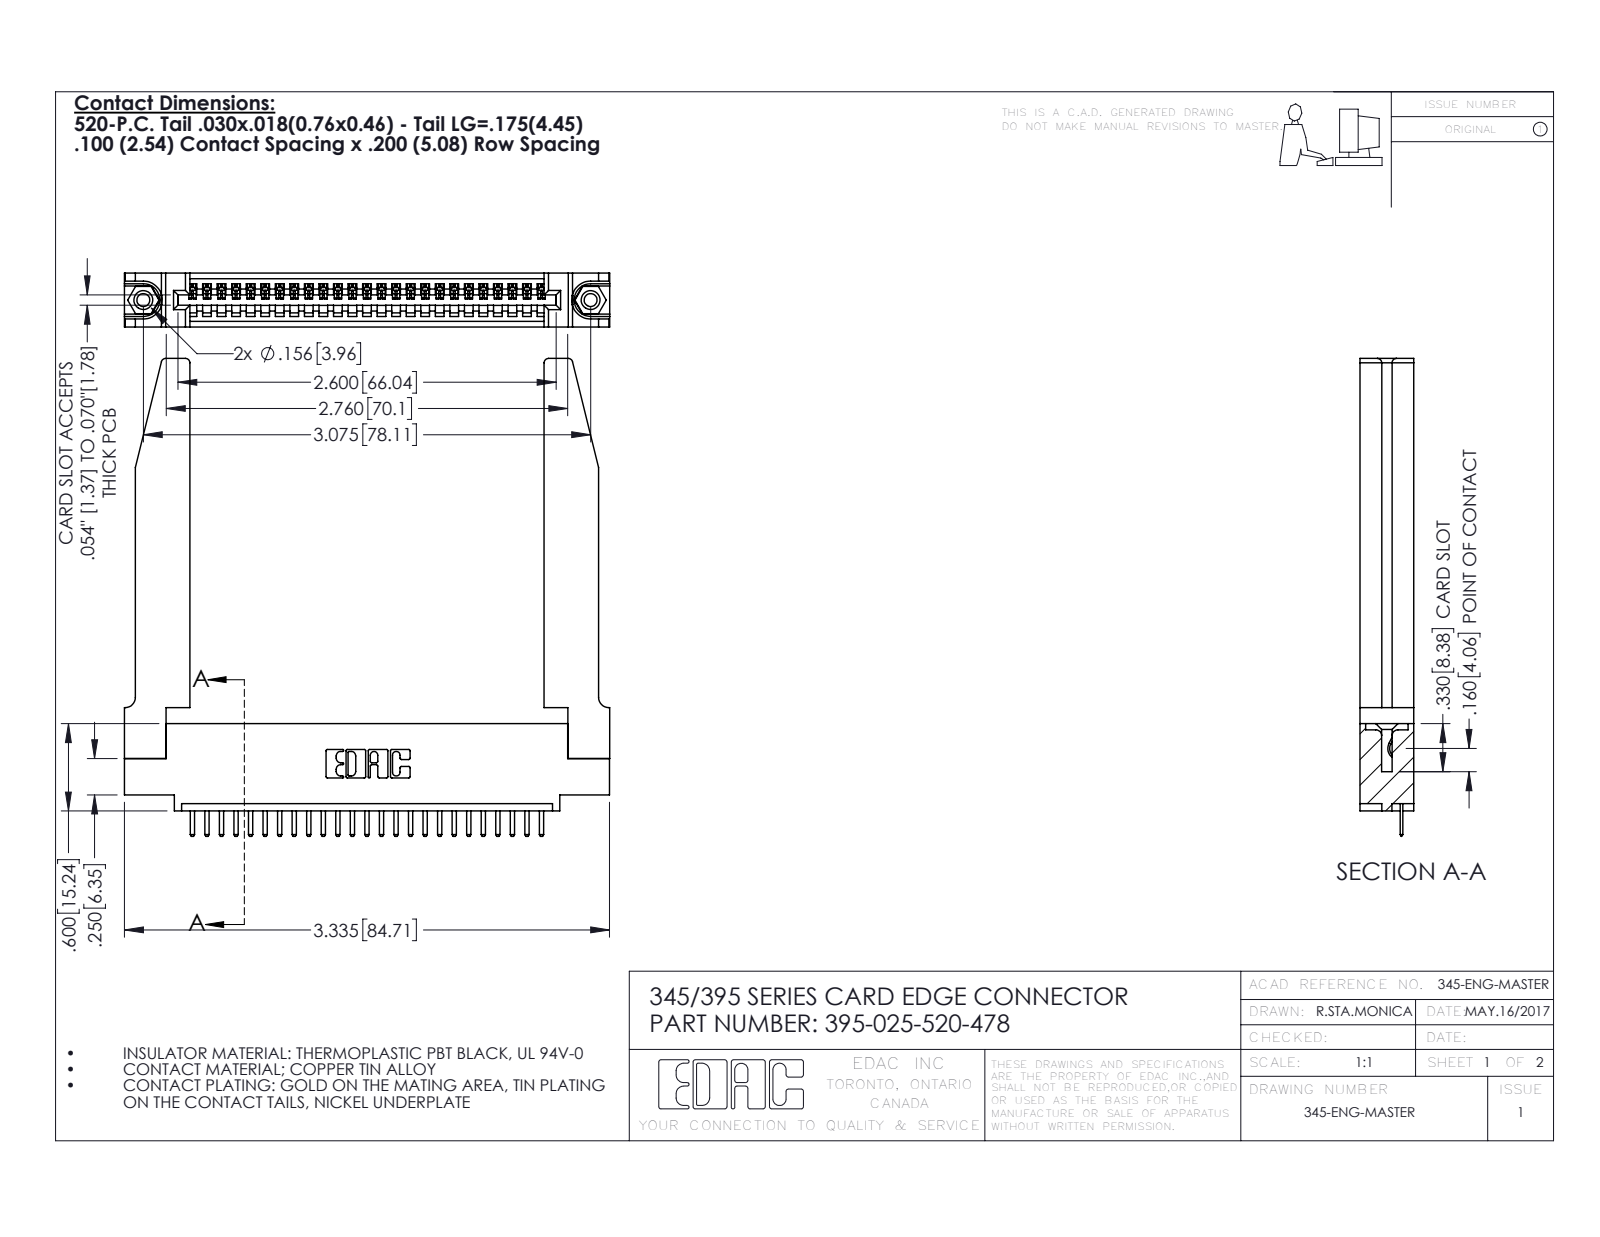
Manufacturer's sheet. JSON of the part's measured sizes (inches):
{"part_name": "395-025-520-478; 345-292-001_345-293-120; 345-250-001_345-250-001-102; 345-220-078_345-220-078 (+1 more)", "step_written_by": "SolidWorks 2016 (CONFIG_CONTROL_DESIGN)", "units": "inches", "bodies": {"solids": 30, "faces": 1914, "planar": 1276, "cylindrical": 586, "other": 52}, "overall_size": [3.336, 3.285, 0.37], "volume_in3": 0.948, "surface_area_in2": 26.01, "round_holes": [[0.089, 2], [0.125, 2], [0.156, 2], [0.064, 1]], "round_bosses_or_shafts": [[0.155, 2]], "partial_cylinders_radius": [[0.01, 52], [0.006, 50], [0.01, 22], [0.03, 8], [0.007, 6], [0.031, 6], [0.026, 3], [0.031, 2]], "face_to_face_distances": [0.37, 0.072, 0.298, 0.2, 0.098, 0.272, 0.025, 0.148, 0.15, 0.225], "hole_center_spacings": [0.27, 2.84, 3.075]}
